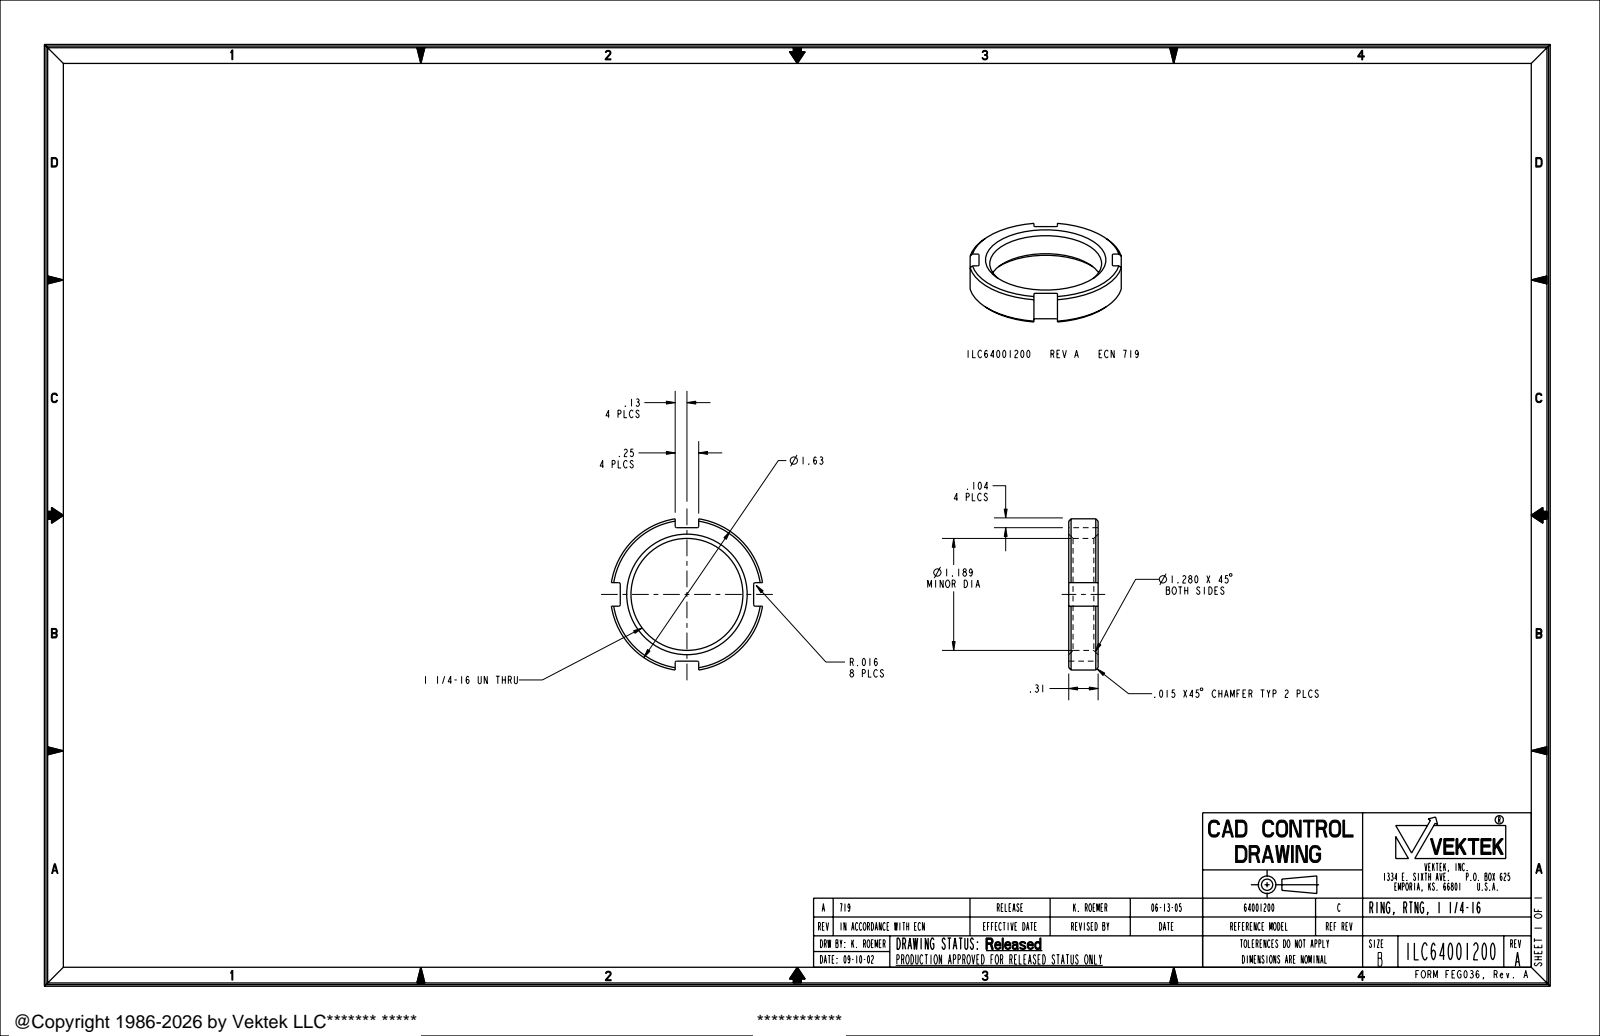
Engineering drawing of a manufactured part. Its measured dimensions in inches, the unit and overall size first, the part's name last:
Units: inches
Overall size (bounding box): 1.625 × 1.625 × 0.312
Round holes (diameter × count): ⌀1.189 ×1
Round bosses / shafts (diameter × count): ⌀1.625 ×1
Partial cylindrical surfaces — rounded edges, fillets, slot ends (radius × count): R0.016 ×8
Main face-to-face distances: 0.312, 0.833, 0.583, 1.417, 0.25
Volume: 0.259 in³ · Surface area: 4.383 in²
Bodies: 1 solid, 40 faces (14 planar, 14 cylindrical, 12 other)
Part name (STEP PRODUCT): ILC64001200
STEP written by: PRO/ENGINEER BY PARAMETRIC TECHNOLOGY CORPORATION, 2004290 (AUTOMOTIVE_DESIGN_CC2)
